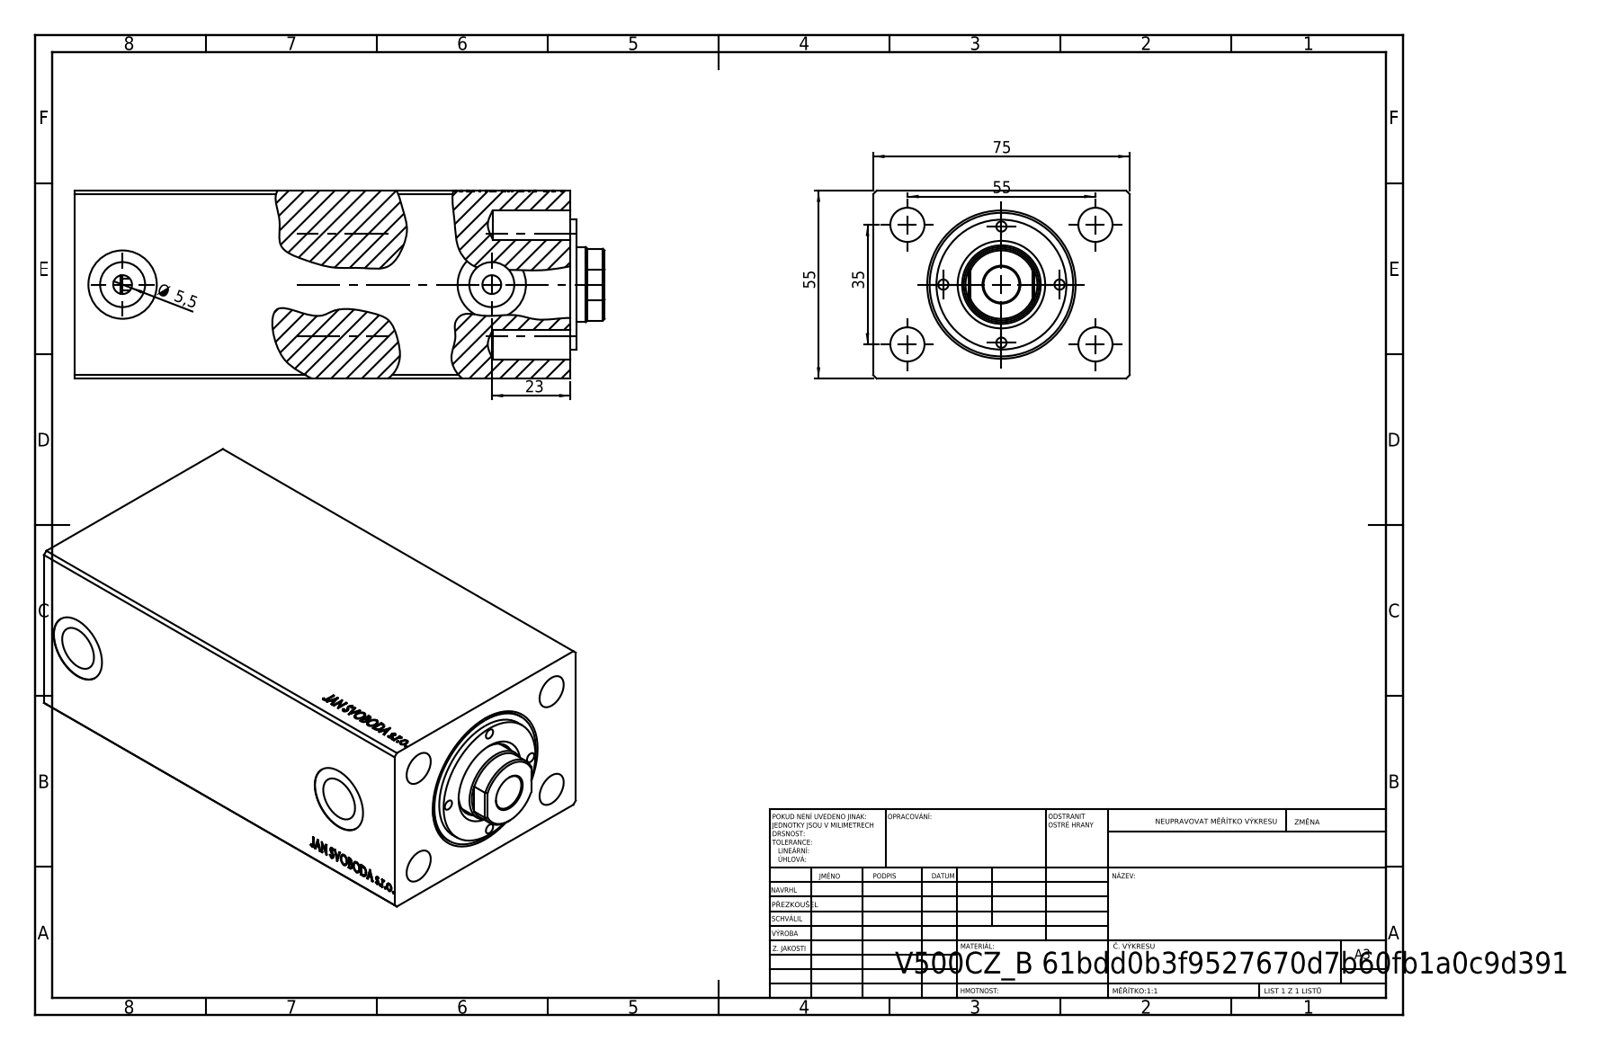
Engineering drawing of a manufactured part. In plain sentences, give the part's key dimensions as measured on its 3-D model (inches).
The part is named "V500CZ; V500CZ_B_VC". Its 3-D file was written by "SolidWorks 2019 (CONFIG_CONTROL_DESIGN)". It is 3 solids with 873 faces: 399 planar, 58 cylindrical and 416 other. Overall it measures 6.102 by 2.953 by 2.165 inches. Its volume is 34.39 cubic inches and its surface area 149.8 square inches. Round holes: 4 of diameter 0.118, 4 of diameter 0.394, 2 of diameter 0.217, 2 of diameter 0.518, 2 of diameter 0.787, 1 of diameter 0.413, 1 of diameter 0.866, 1 of diameter 0.906, 1 of diameter 1.26, 1 of diameter 1.417, 1 of diameter 1.654. Round bosses or shafts: 1 of diameter 1.496. Partial cylindrical surfaces (rounded edges, fillets, slot ends): 1 of radius 0.413. The main face-to-face distances are 2.165, 2.953, 5.709, 0.531, 5.177, 2.618, 2.559, 3.15, 5.701, 3.142. The hole center spacings are 0.669, 0.804, 0.946, 1.083, 1.283, 1.737, 1.883, 1.339.
